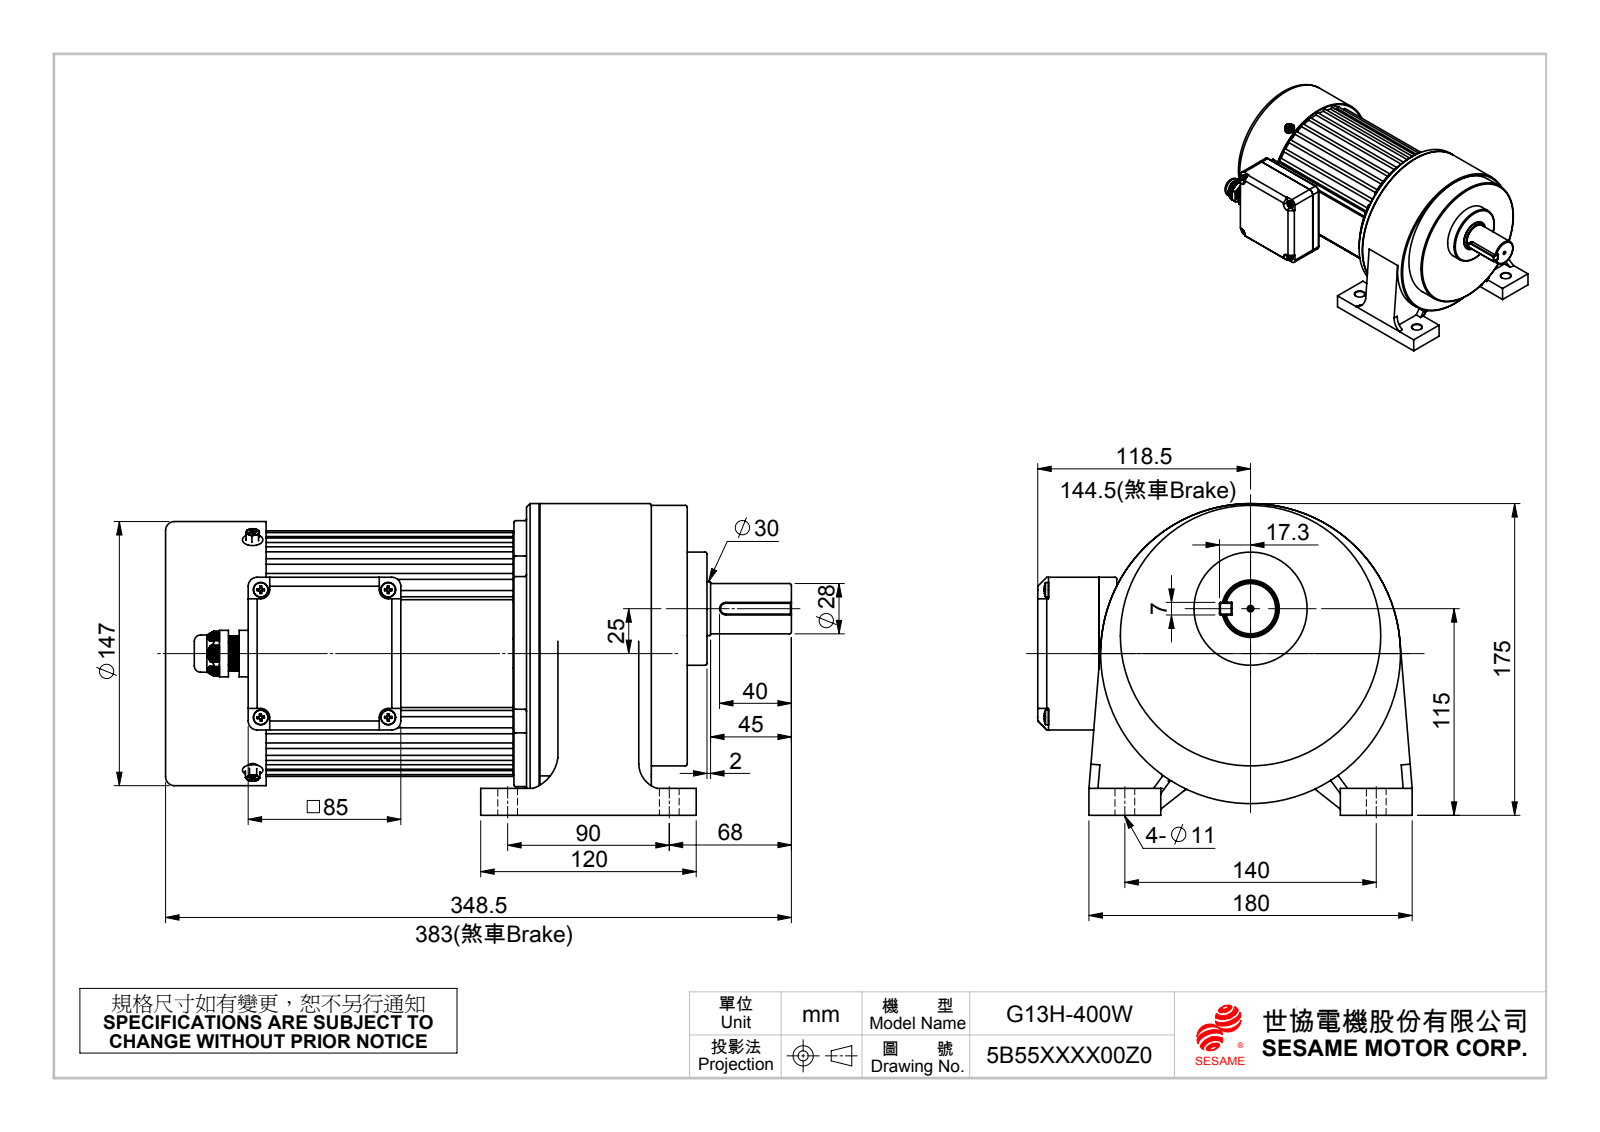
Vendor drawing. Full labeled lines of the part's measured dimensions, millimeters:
Part name (STEP PRODUCT): M400C1A; 出線盒墊片JTH-UP3(PVC2mm厚); G13-750C1-04(含200.400)_G13400C1成品; 出線盒上蓋 (+8 more)
STEP written by: SolidWorks 2010 (CONFIG_CONTROL_DESIGN)
Units: millimetres
Bodies: 19 solids, 2793 faces (866 planar, 852 cylindrical, 1075 other)
Overall size (bounding box): 348.5 × 208.5 × 173.5
Volume: 4 846 000 mm³ · Surface area: 489 295 mm²
Round holes (diameter × count): ⌀5 ×14, ⌀3.3 ×9, ⌀8 ×9, ⌀5.1 ×5, ⌀6 ×5, ⌀11 ×4, ⌀2 ×1, ⌀10.8 ×1, ⌀16.5 ×1, ⌀30 ×1, ⌀31 ×1, ⌀32 ×1
Round bosses / shafts (diameter × count): ⌀8.3 ×4, ⌀4 ×4, ⌀5 ×2, ⌀167 ×1, ⌀148 ×1, ⌀147 ×1, ⌀145 ×1, ⌀132 ×1
Partial cylindrical surfaces — rounded edges, fillets, slot ends (radius × count): R1 ×55, R1.85 ×31, R0.5 ×24, R3 ×8, R5 ×8, R2.75 ×6, R8 ×5, R2 ×4
Main face-to-face distances: 20, 140, 77, 160, 44, 12, 1, 65.5, 148, 21.5
Hole centre spacings: 144.57, 45, 63.67, 71, 76.01, 11, 11.5, 14.6
